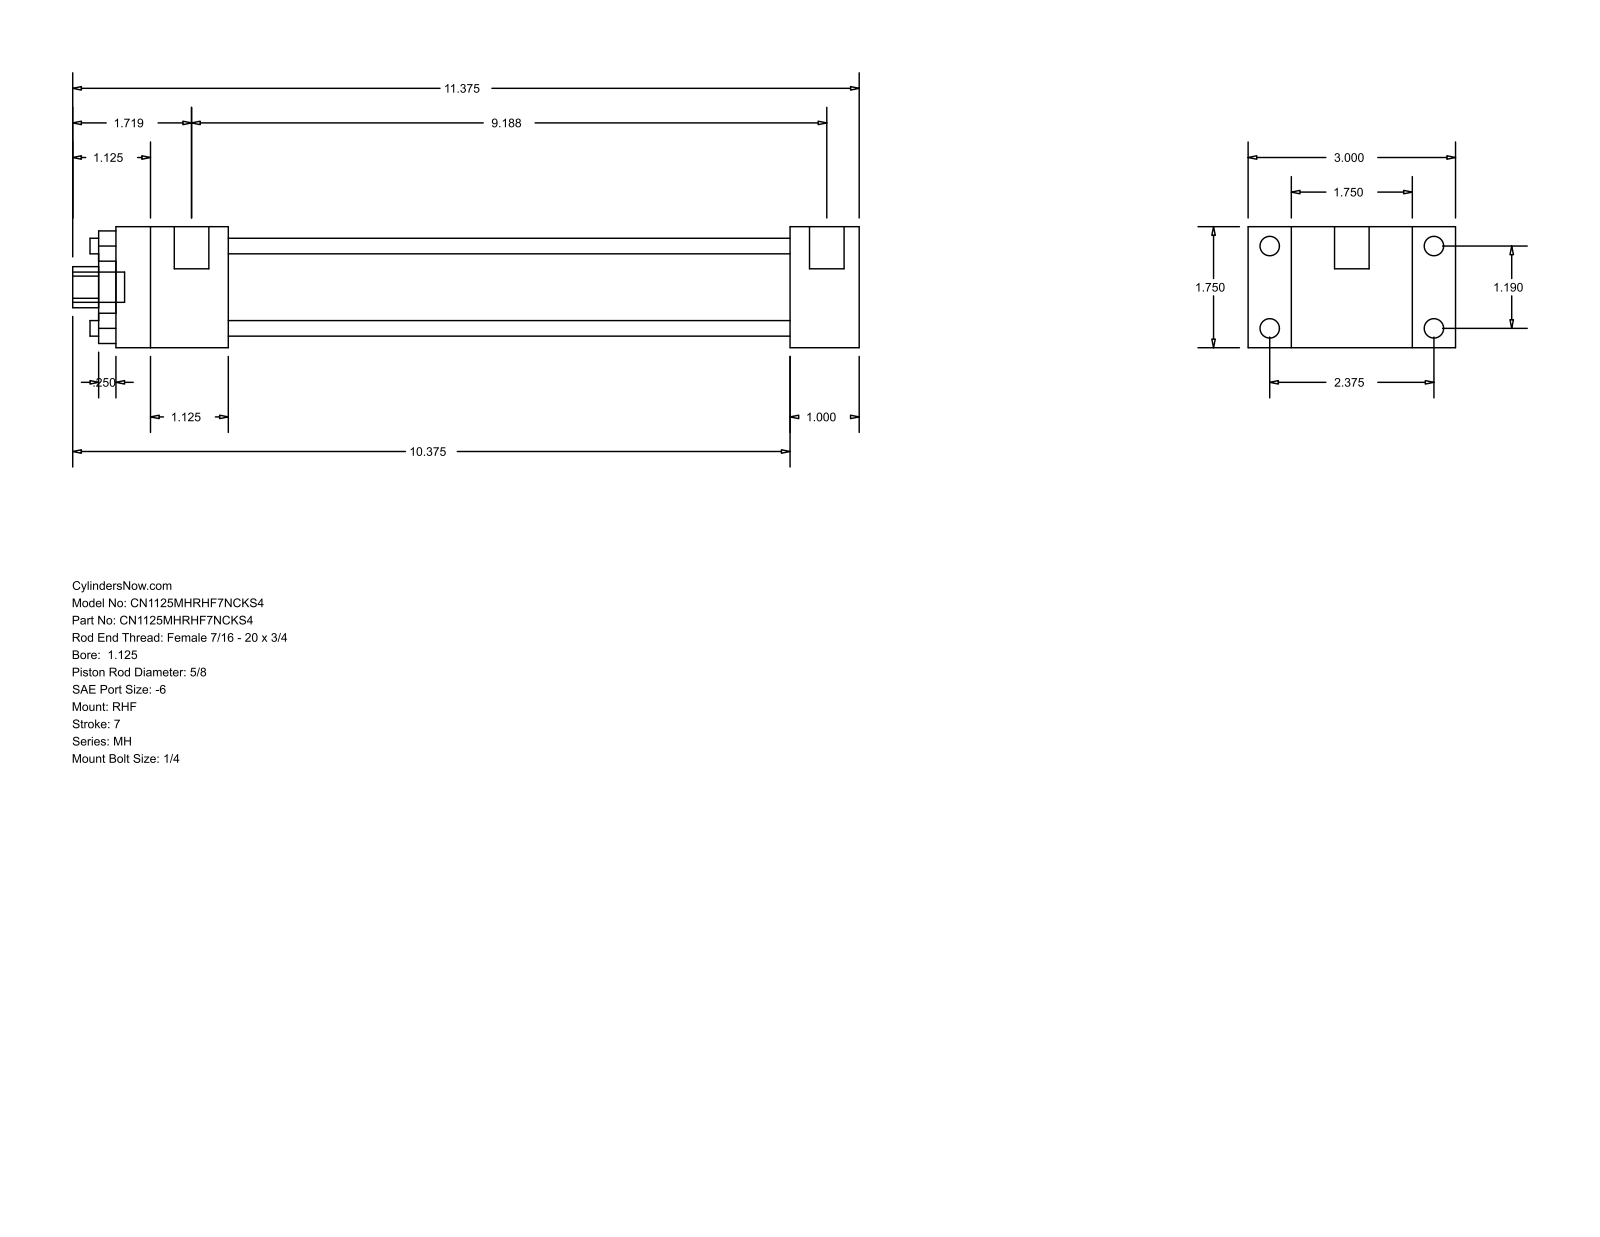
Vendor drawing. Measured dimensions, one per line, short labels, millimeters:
name: MH_RHF__0112_0.625
written by: GSSL Pune (CONFIG_CONTROL_DESIGN)
unit: mm
bodies: 0 solids, 88 faces (60 planar, 28 cylindrical, 0 other)
size: 288.93 × 76.2 × 44.45
holes: 4× ⌀5.71, 1× ⌀15.88, 1× ⌀28.57, 1× ⌀34.92
bosses: 4× ⌀7.14, 4× ⌀5.56, 2× ⌀12.7, 1× ⌀11.11
rounds: 1× R7.54
face distances: 44.46, 15.87, 60.33, 25.41, 76.2, 206.37, 231.78, 41.27, 247.64, 273.05
hole spacings: 21.37, 30.22, 42.74
